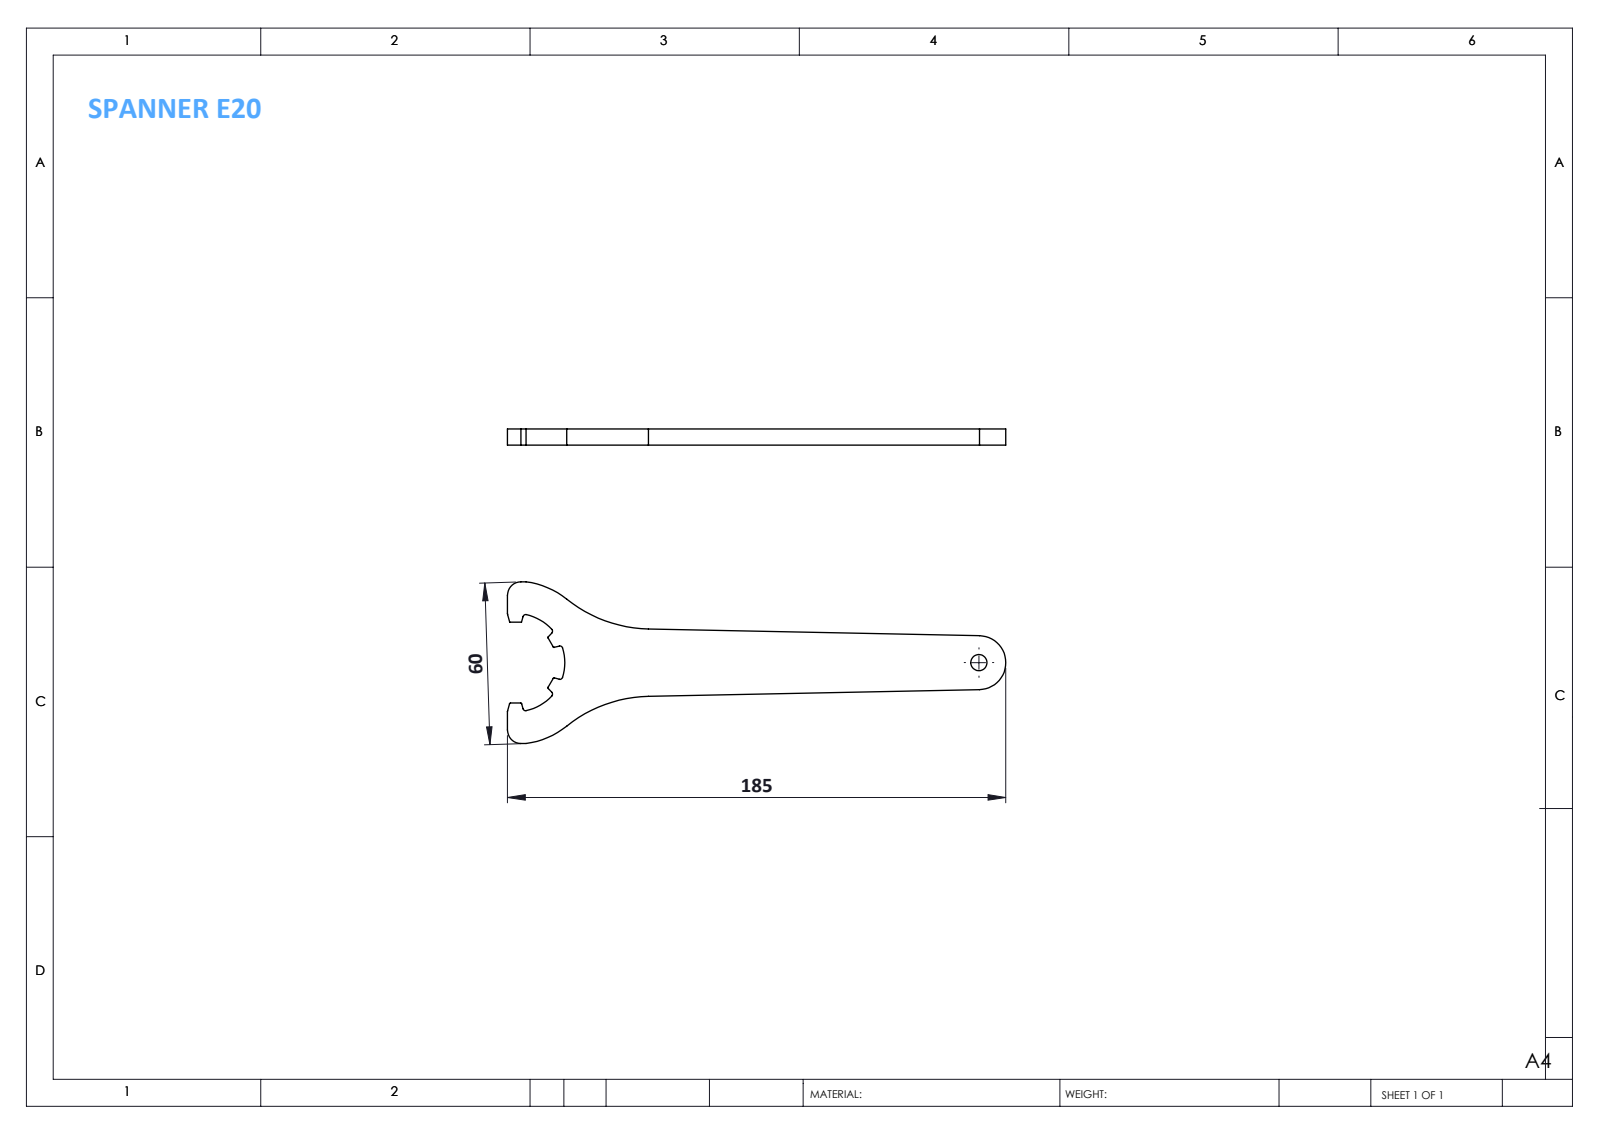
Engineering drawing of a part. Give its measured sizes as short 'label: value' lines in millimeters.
name: SPANNER E20
written by: SolidWorks 2014 (CONFIG_CONTROL_DESIGN)
unit: mm
bodies: 1 solid, 50 faces (20 planar, 30 cylindrical, 0 other)
size: 185 × 60 × 6
volume: 27 239 mm³; area: 12 122 mm²
holes: 1× ⌀6
rounds: 8× R1, 6× R0.4, 2× R5, 2× R50, 1× R10, 1× R18.25, 1× R30.25
face distances: 6, 3.52, 30, 15, 45, 60
